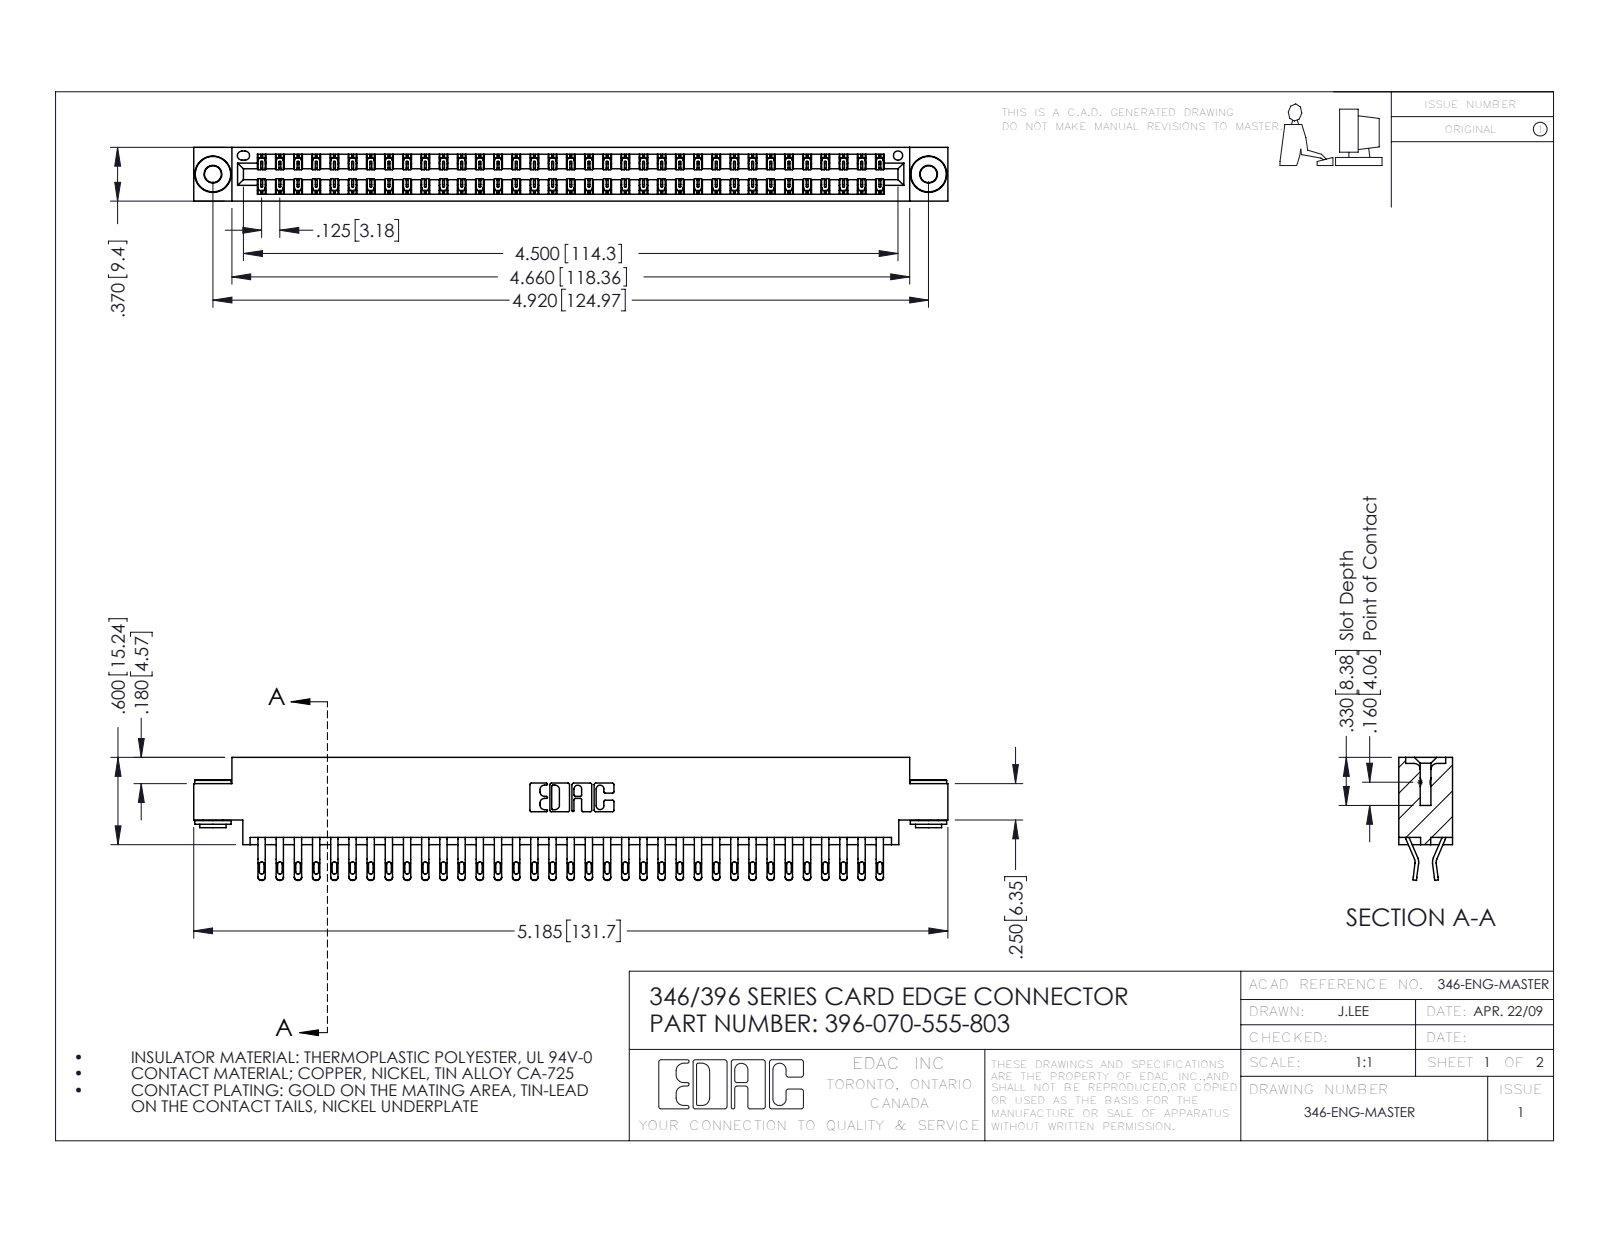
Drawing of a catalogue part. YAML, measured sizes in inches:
part_name: "345-250-002_345-250-002-102; 396-070-555-803; 345-292-001_555 Tail; 346 Part_0.170 Offset - 0.156 Dia-TH"
step_written_by: "SolidWorks 2016 (CONFIG_CONTROL_DESIGN)"
units: inches
bodies: {solids: 73, faces: 4224, planar: 2400, cylindrical: 1816, other: 8}
overall_size: [5.185, 0.845, 0.37]
volume: 0.785
surface_area: 28.95
round_holes:
  - {diameter: 0.116, count: 2}
  - {diameter: 0.156, count: 2}
  - {diameter: 0.064, count: 1}
round_bosses_or_shafts:
  - {diameter: 0.25, count: 2}
  - {diameter: 0.18, count: 2}
  - {diameter: 0.136, count: 2}
partial_cylinders:
  - {radius: 0.016, count: 140}
  - {radius: 0.02, count: 140}
  - {radius: 0.006, count: 105}
  - {radius: 0.01, count: 22}
  - {radius: 0.007, count: 6}
  - {radius: 0.031, count: 6}
  - {radius: 0.026, count: 3}
  - {radius: 0.01, count: 2}
face_to_face_distances: [0.048, 0.322, 0.37, 0.25, 0.025, 0.275, 0.072, 0.298, 0.148, 0.222]
hole_center_spacings: [0.246, 4.711, 4.92]
